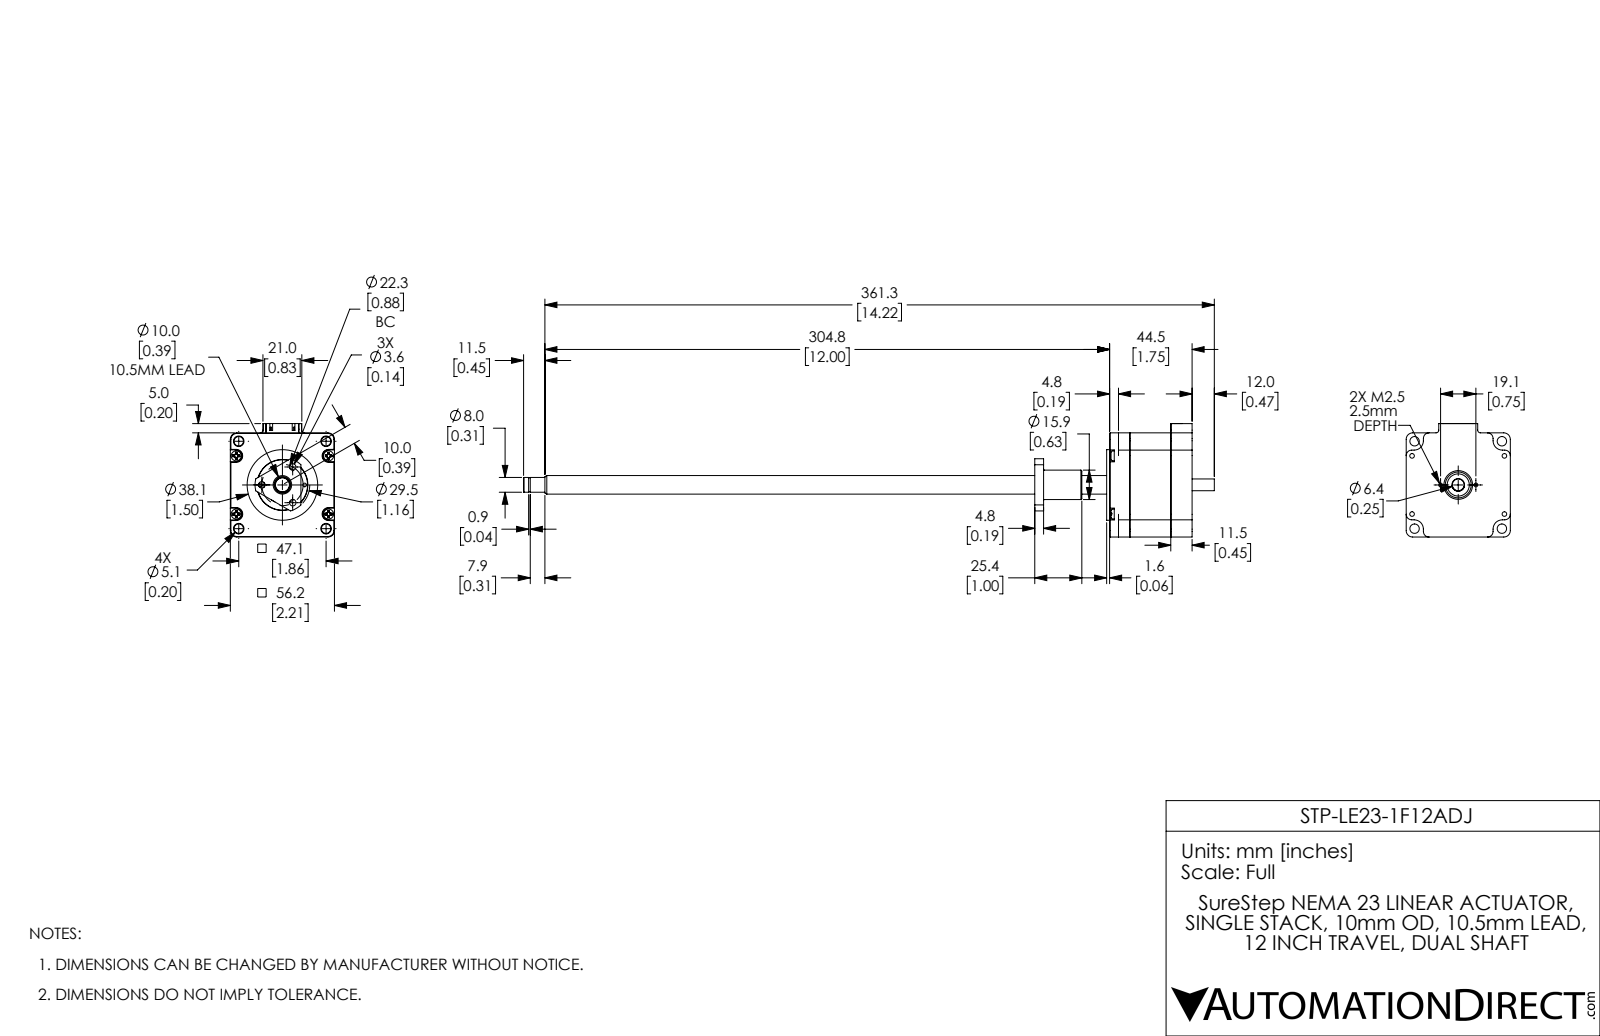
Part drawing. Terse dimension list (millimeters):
name: STP-LE23-1F12ADJ; STP-LE23-1F12ADJ_1; STP-LE23-1F12ADJ_2
written by: SolidWorks 2017 (AUTOMOTIVE_DESIGN)
unit: mm
bodies: 8 solids, 749 faces (305 planar, 202 cylindrical, 242 other)
size: 372.8 × 61.22 × 56.2
volume: 129 337 mm³; area: 53 297 mm²
holes: 8× ⌀4.5, 4× ⌀2.5, 4× ⌀3.3, 4× ⌀5.1, 3× ⌀3.56, 2× ⌀2, 2× ⌀2.05, 1× ⌀6.8, 1× ⌀8.5, 1× ⌀12, 1× ⌀15.5, 1× ⌀20
bosses: 4× ⌀5.4, 1× ⌀38.1, 1× ⌀36, 1× ⌀35.6, 1× ⌀34.85, 1× ⌀16, 1× ⌀15.88, 1× ⌀10
rounds: 10× R1.5, 8× R3, 4× R1.8, 4× R3.2, 4× R3.5, 4× R5, 1× R14.75, 1× R19.3
face distances: 22, 44.5, 56.2, 11.5, 33.5, 1.6, 11, 33, 51.4, 2.4
hole spacings: 14.12, 24.75, 33.05, 35.01, 45.74, 48.53, 56.99, 6.55
